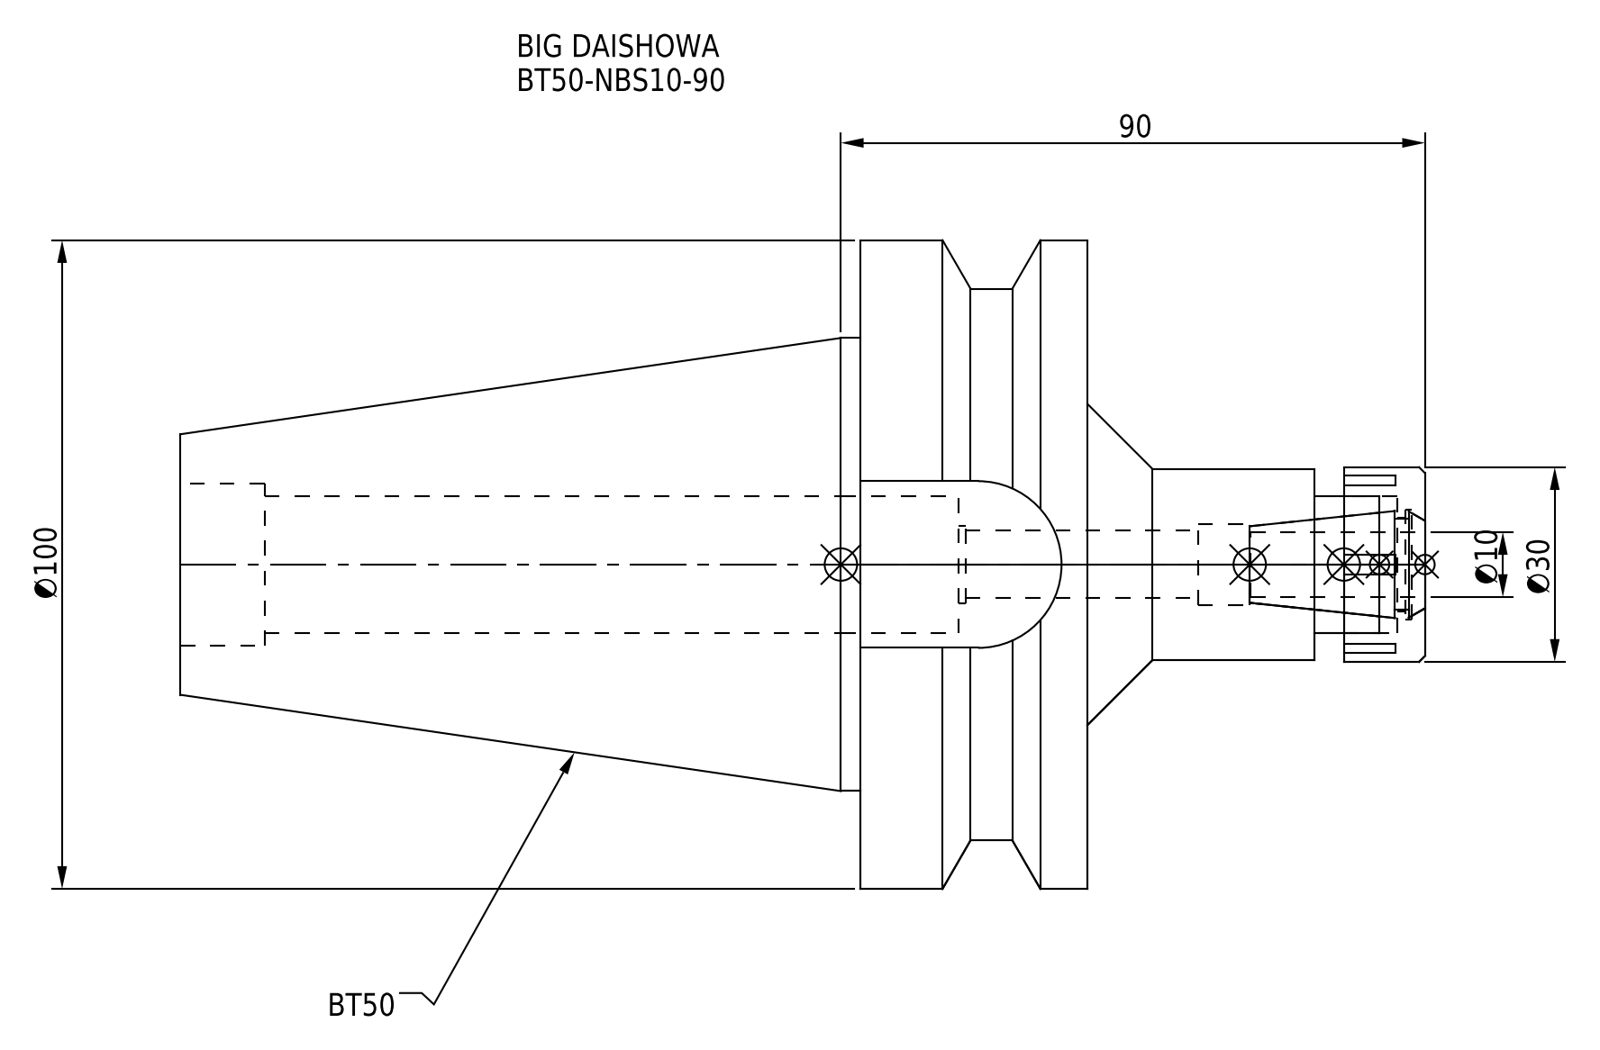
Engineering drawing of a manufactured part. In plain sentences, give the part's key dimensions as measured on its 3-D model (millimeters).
The part is named "DXF_TEMP_ASSY_ASM_4_ASM.stp; BT50-NBS10-90_1.stp; BT50-NBS10-90; NBN10_1.stp (+3 more)". Its 3-D file was written by "SolidWorks 2019 (CONFIG_CONTROL_DESIGN)". It is 2 solids with 93 faces: 45 planar, 34 cylindrical and 14 other. Overall it measures 191.8 by 100 by 100 millimeters. Its volume is 480 648 cubic millimeters and its surface area 62 209 square millimeters. Round holes: 1 of diameter 10.4, 1 of diameter 12, 1 of diameter 12.5, 1 of diameter 14.5, 1 of diameter 17, 1 of diameter 21, 1 of diameter 21.2, 1 of diameter 25. Round bosses or shafts: 1 of diameter 100, 1 of diameter 85, 1 of diameter 69.85, 1 of diameter 30, 1 of diameter 29.5. Partial cylindrical surfaces (rounded edges, fillets, slot ends): 1 of radius 12.85. The main face-to-face distances are 35, 139.8, 104.8, 70.8, 52, 87, 191.8, 25.7, 17, 4.5.
